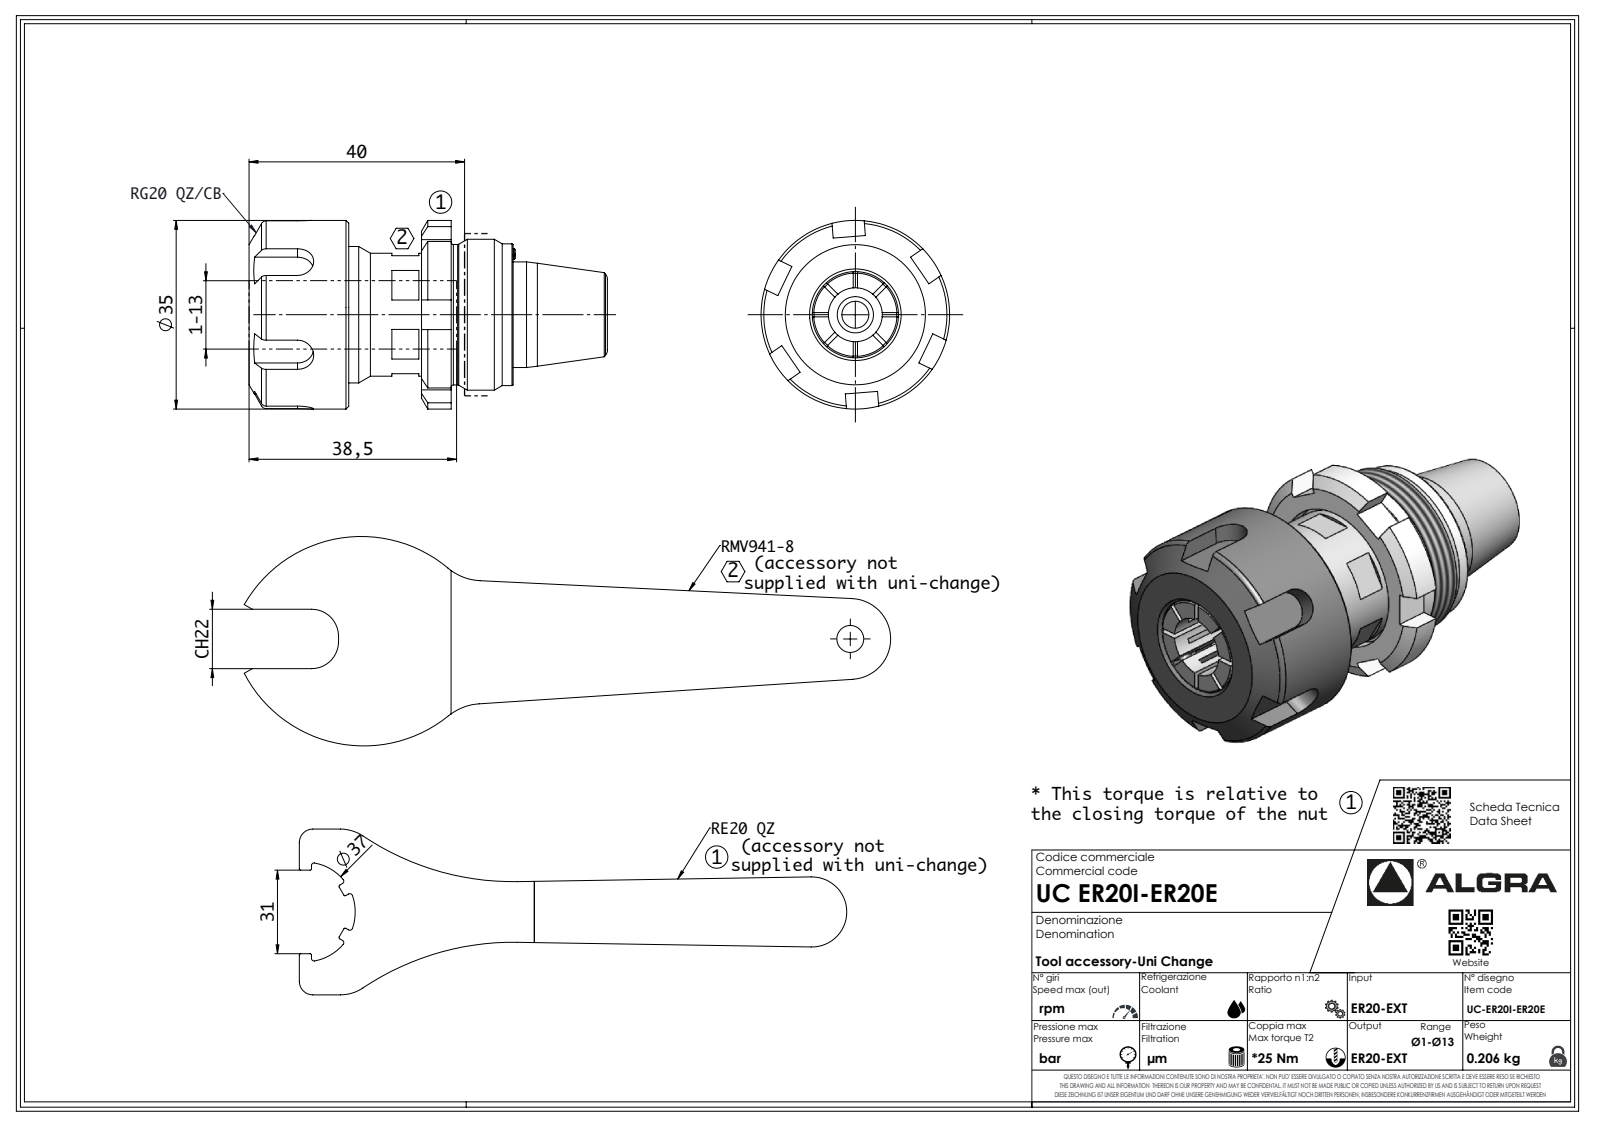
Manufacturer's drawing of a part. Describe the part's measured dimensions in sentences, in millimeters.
The part is named "UCER20I-ER20E". Its 3-D file was written by "SolidWorks 2016 (AUTOMOTIVE_DESIGN)". It is 1 solid with 380 faces: 250 planar, 45 cylindrical and 85 other. Overall it measures 66.52 by 35 by 35 millimeters. Its volume is 37 688 cubic millimeters and its surface area 8 513 square millimeters. Round holes: 1 of diameter 1.57. Round bosses or shafts: 1 of diameter 35, 1 of diameter 28, 1 of diameter 26.3, 1 of diameter 26.05, 1 of diameter 25.3, 1 of diameter 22.8, 1 of diameter 19.6, 1 of diameter 4.77. Partial cylindrical surfaces (rounded edges, fillets, slot ends): 7 of radius 0.25, 7 of radius 0.39, 7 of radius 2.78, 5 of radius 3, 1 of radius 0.16. The main face-to-face distances are 29, 18.5, 5.5, 13.52, 32.02, 19.02, 37.52, 11.5, 17, 30.52.
